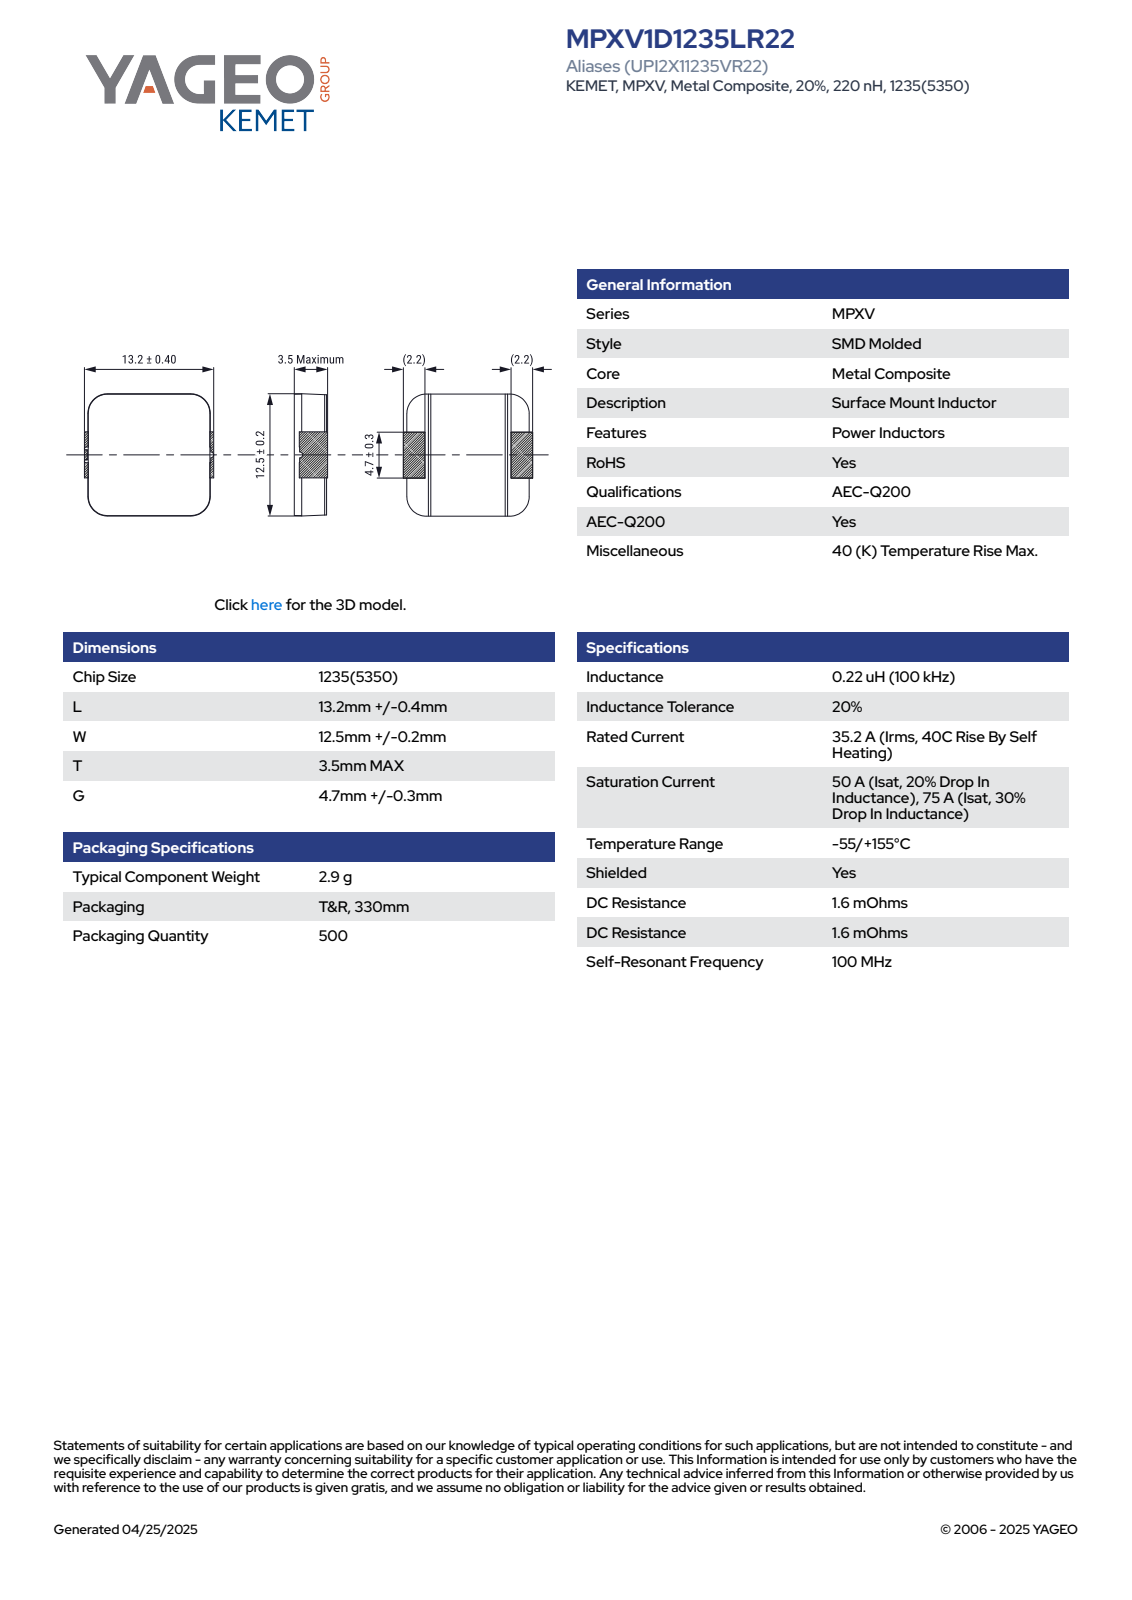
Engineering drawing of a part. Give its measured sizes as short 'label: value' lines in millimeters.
name: MPX1D1235(4_7)(KEMET)
written by: SolidWorks 2018 (AUTOMOTIVE_DESIGN)
unit: mm
bodies: 1 solid, 122 faces (105 planar, 17 cylindrical, 0 other)
size: 13.6 × 12.7 × 3.56
volume: 546 mm³; area: 539 mm²
rounds: 4× R0.26, 4× R1.96, 4× R2, 3× R0.15
face distances: 3.5, 3.3, 13.34, 3.56, 13.6, 13.08, 2.6, 2.54, 2.34, 0.96
